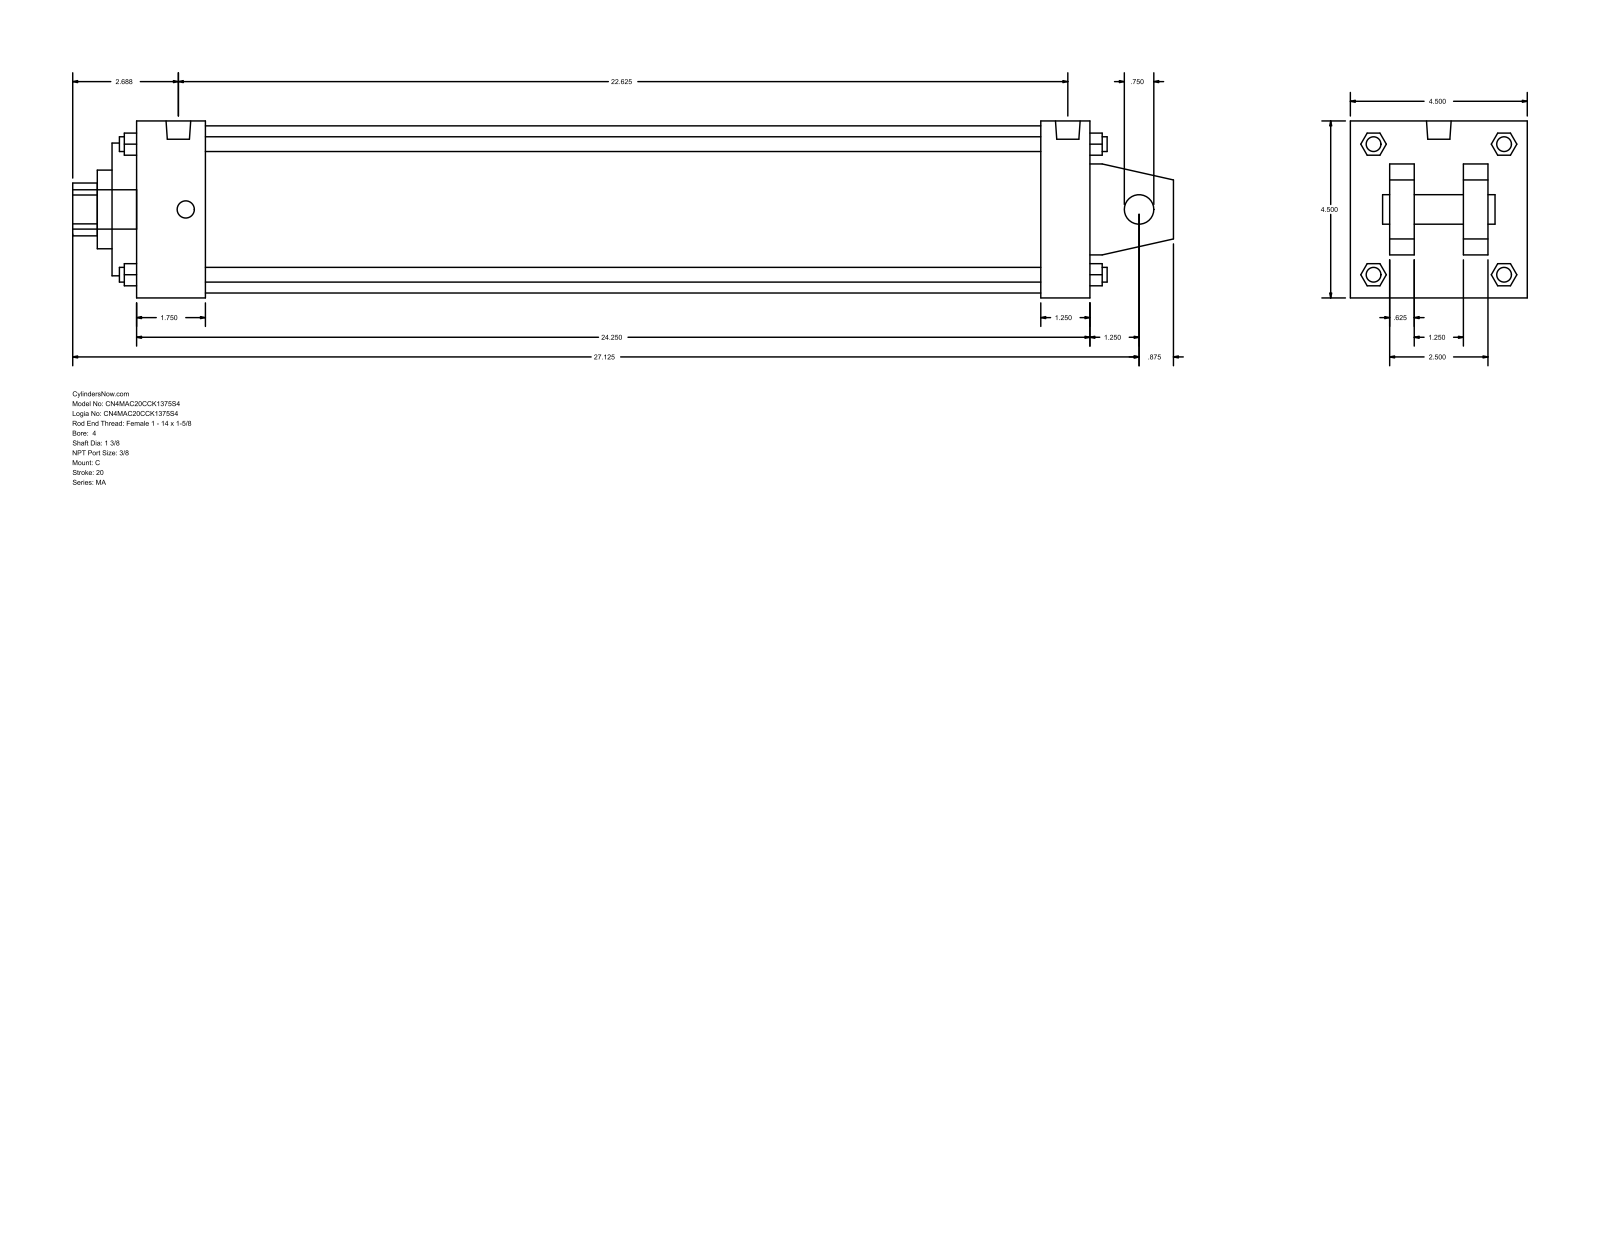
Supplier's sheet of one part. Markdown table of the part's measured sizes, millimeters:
| quantity | value |
| --- | --- |
| part name | MA_C__0400_1.375 |
| STEP written by | GSSL Pune (CONFIG_CONTROL_DESIGN) |
| units | millimeters |
| bodies | 0 solids, 141 faces (109 planar, 32 cylindrical, 0 other) |
| overall size | 711.2 × 114.3 × 114.3 |
| round holes (diameter × count) | 19.05 × 1, 34.92 × 1, 50.8 × 1, 85.72 × 1, 107.95 × 1 |
| round bosses / shafts (diameter × count) | 11.11 × 4, 9.53 × 4, 15.93 × 2, 25.4 × 1 |
| partial cylindrical surfaces (radius × count) | 17.06 × 1 |
| main face-to-face distances | 114.3, 15.87, 615.96, 73.03, 41.27, 25.4, 88.9, 47.63, 631.83, 600.08 |
